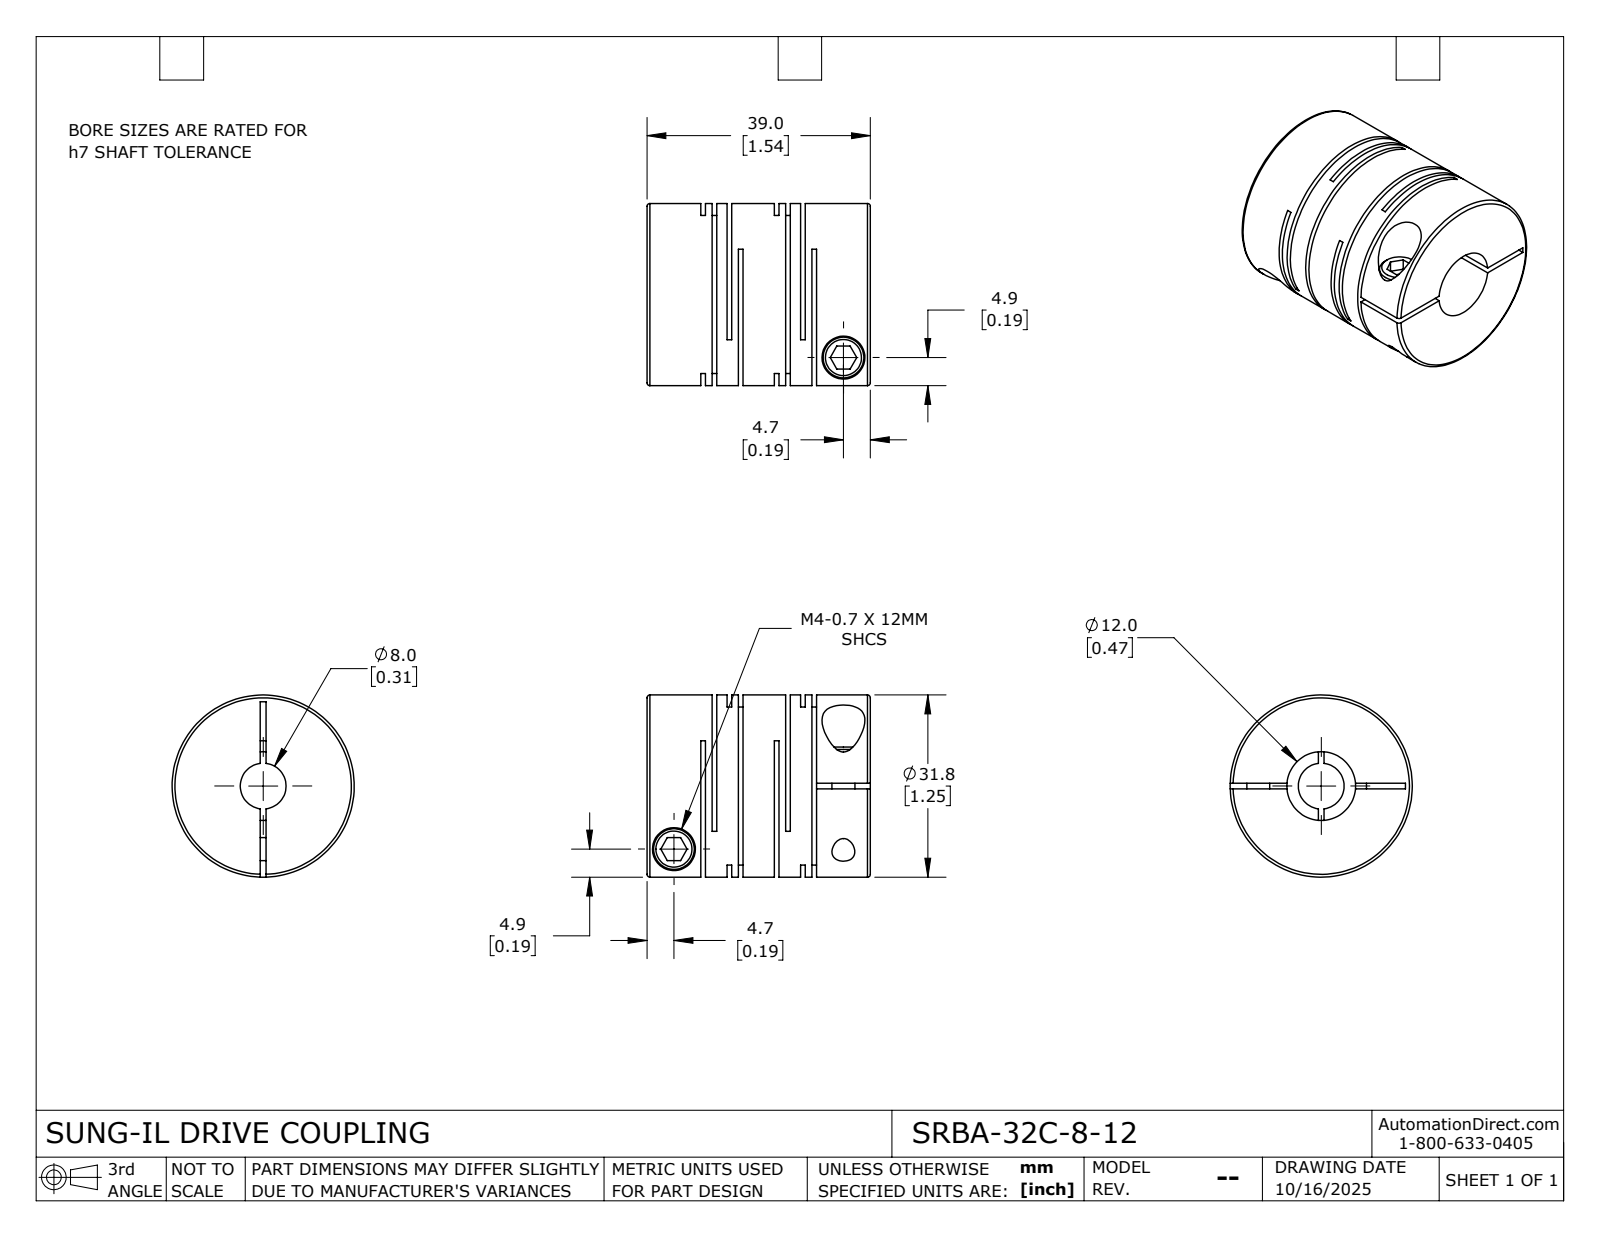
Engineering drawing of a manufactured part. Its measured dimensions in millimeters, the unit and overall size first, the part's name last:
Units: millimetres
Overall size (bounding box): 39 × 31.8 × 31.8
Round holes (diameter × count): ⌀4 ×2, ⌀7.5 ×2, ⌀8 ×1, ⌀12 ×1
Round bosses / shafts (diameter × count): ⌀7.1 ×2, ⌀31.8 ×1
Main face-to-face distances: 0.8, 12.84, 1.98, 4.58, 12.04, 1.18, 10.86, 3.78, 8.26, 2.6
Volume: 22 893 mm³ · Surface area: 15 795 mm²
Bodies: 1 solid, 115 faces (60 planar, 42 cylindrical, 13 other)
Part name (STEP PRODUCT): SRBA-32C-8-12
STEP written by: SolidWorks 2024 (CONFIG_CONTROL_DESIGN)
